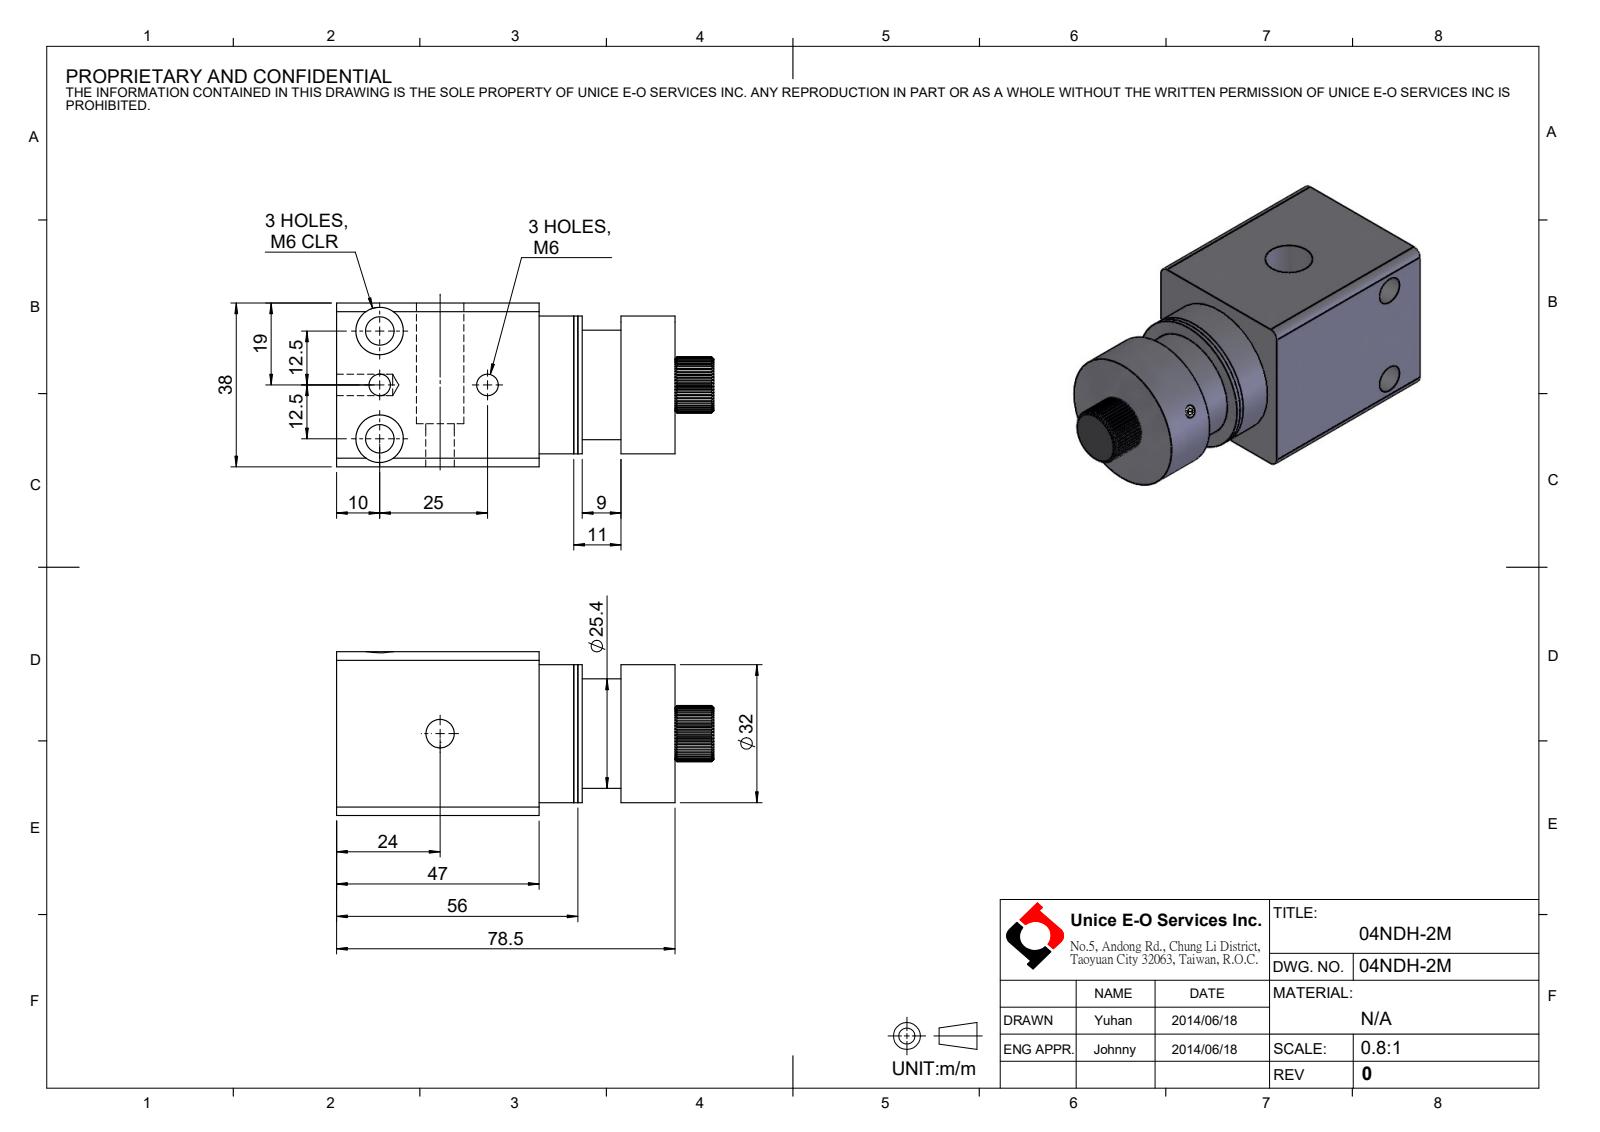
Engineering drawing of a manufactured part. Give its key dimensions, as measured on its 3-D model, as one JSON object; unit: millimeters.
{"part_name": "04NDH-2M", "step_written_by": "SolidWorks 2016 (CONFIG_CONTROL_DESIGN)", "units": "millimeters", "bodies": {"solids": 6, "faces": 253, "planar": 133, "cylindrical": 100, "other": 20}, "overall_size": [87.5, 38, 38], "volume_mm3": 81509, "surface_area_mm2": 22761, "round_holes": [[5, 3], [6.6, 3], [11, 3], [2.5, 1], [6.5, 1], [25.4, 1], [25.6, 1]], "round_bosses_or_shafts": [[32, 1], [6, 1], [3, 1]], "partial_cylinders_radius": [[2, 4], [6.5, 1]], "face_to_face_distances": [38, 10, 9, 76, 1, 78.5, 2.5, 31.5, 47, 29], "hole_center_spacings": [12.5, 25, 27.95]}
